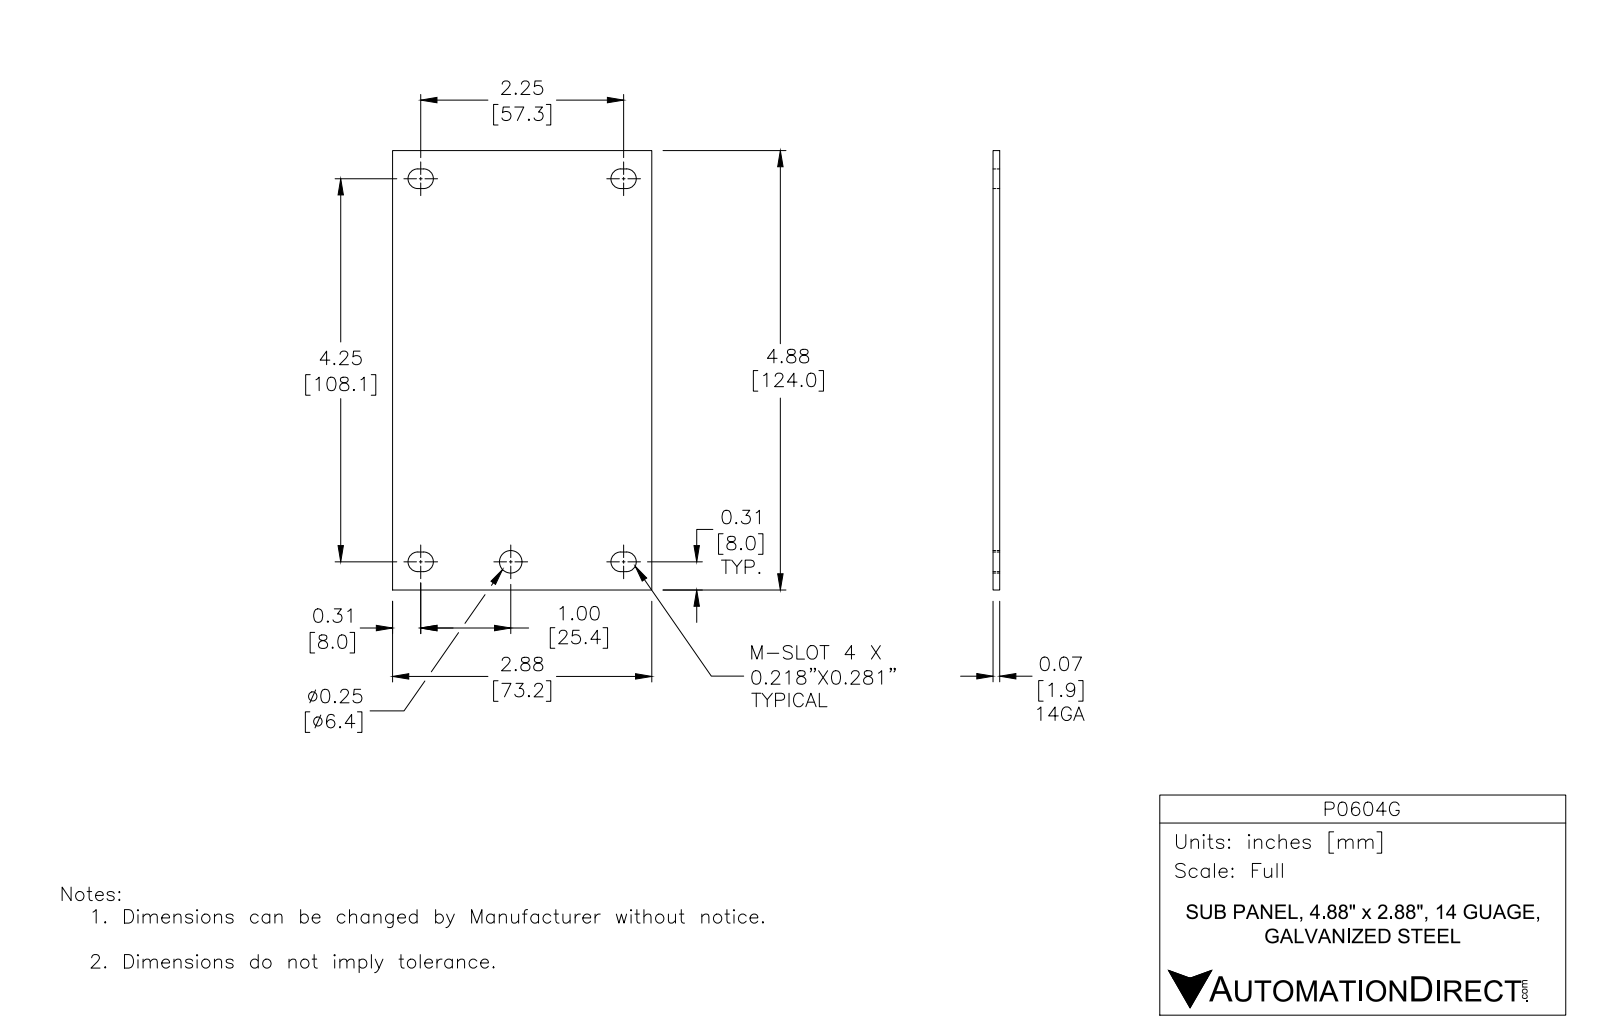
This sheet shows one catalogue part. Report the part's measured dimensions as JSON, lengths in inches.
{"part_name": "P0604G", "step_written_by": "Autodesk Inventor 2012 (AUTOMOTIVE_DESIGN)", "units": "inches", "bodies": {"solids": 1, "faces": 23, "planar": 14, "cylindrical": 9, "other": 0}, "overall_size": [4.88, 2.88, 0.074], "volume_in3": 1.021, "surface_area_in2": 29.05, "round_holes": [[0.25, 1]], "partial_cylinders_radius": [[0.109, 8]], "face_to_face_distances": [0.074, 2.88, 4.88, 0.204, 0.422, 4.458, 4.676, 0.218, 4.254, 4.472]}
